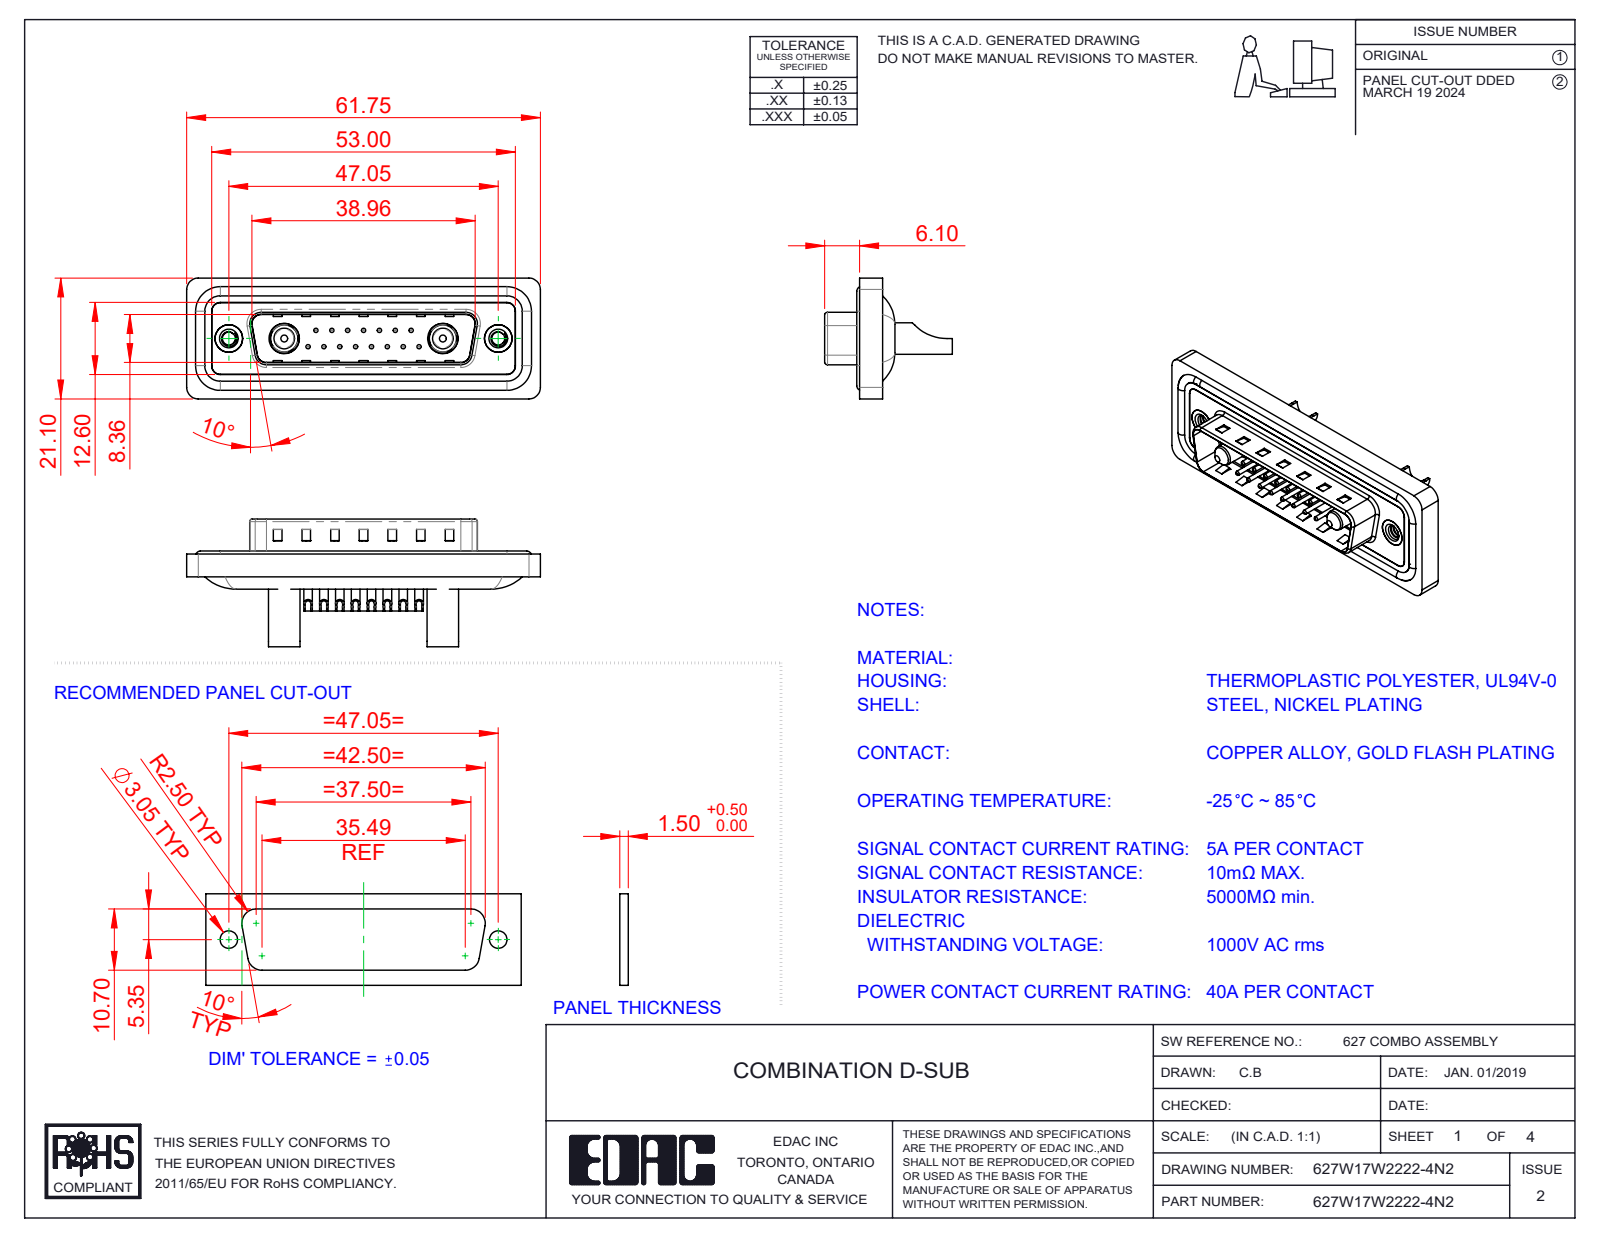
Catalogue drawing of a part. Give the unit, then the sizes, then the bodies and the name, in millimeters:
Units: millimetres
Overall size (bounding box): 61.75 × 22.3 × 21.1
Round holes (diameter × count): ⌀0.75 ×15, ⌀1 ×15, ⌀1.6 ×15, ⌀2 ×15, ⌀2.26 ×2, ⌀4 ×2, ⌀4.6 ×2, ⌀4.8 ×2, ⌀4.85 ×2, ⌀5 ×2, ⌀5.3 ×2
Round bosses / shafts (diameter × count): ⌀1.5 ×15, ⌀1.6 ×4, ⌀5.5 ×2, ⌀5.2 ×2, ⌀4.9 ×2, ⌀4.75 ×2, ⌀3.75 ×2, ⌀3.6 ×2
Partial cylindrical surfaces — rounded edges, fillets, slot ends (radius × count): R1.5 ×22, R2 ×18, R0.5 ×8, R1.6 ×8, R1 ×6, R0.25 ×4, R0.6 ×4, R0.65 ×4
Main face-to-face distances: 0.4, 1.5, 1.1, 1.6, 0.5, 3.1, 2.9, 0.82, 9.58, 4.1
Hole centre spacings: 3.16, 2.77, 5.54, 8.31, 5.04, 7.49, 11.08, 5.03
Volume: 7 369 mm³ · Surface area: 12 313 mm²
Bodies: 26 solids, 1124 faces (368 planar, 468 cylindrical, 288 other)
Part name (STEP PRODUCT): 627Combo Waterproof Housing_25 Contacts; 627Combo Housing_17W2; 627Combo Shell Rear_25 Contacts; 627Combo Shell Front_25 Contacts (+5 more)
STEP written by: SolidWorks 2023 (CONFIG_CONTROL_DESIGN)
